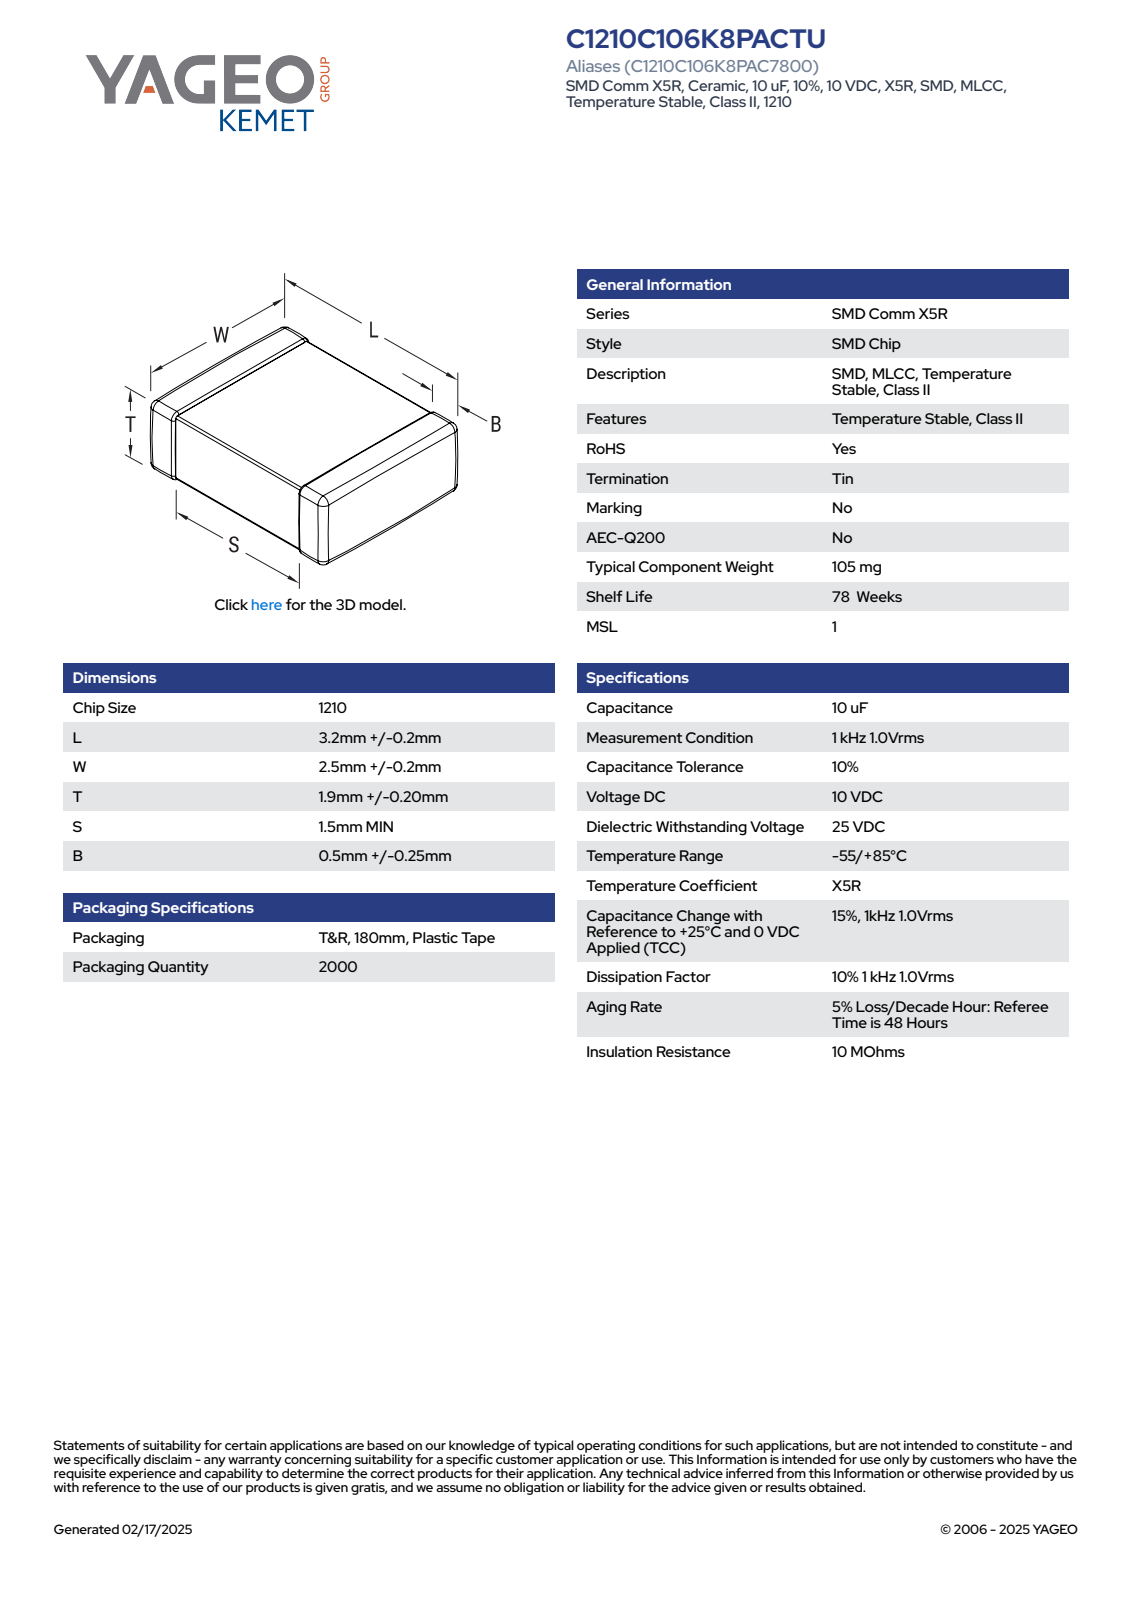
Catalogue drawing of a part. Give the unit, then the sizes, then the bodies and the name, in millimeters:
Units: millimetres
Overall size (bounding box): 3.4 × 2.7 × 2.1
Main face-to-face distances: 2.04, 3.4, 2.64, 1.98, 2.58, 2.1, 2.7, 2.05, 1.99, 1.31
Volume: 18 mm³ · Surface area: 43 mm²
Bodies: 4 solids, 125 faces (71 planar, 38 cylindrical, 16 other)
Part name (STEP PRODUCT): CCS_CCSTDNOS_1210_L3.4W2.7T2.1B0.75
STEP written by: SolidWorks 2014 (AUTOMOTIVE_DESIGN)
